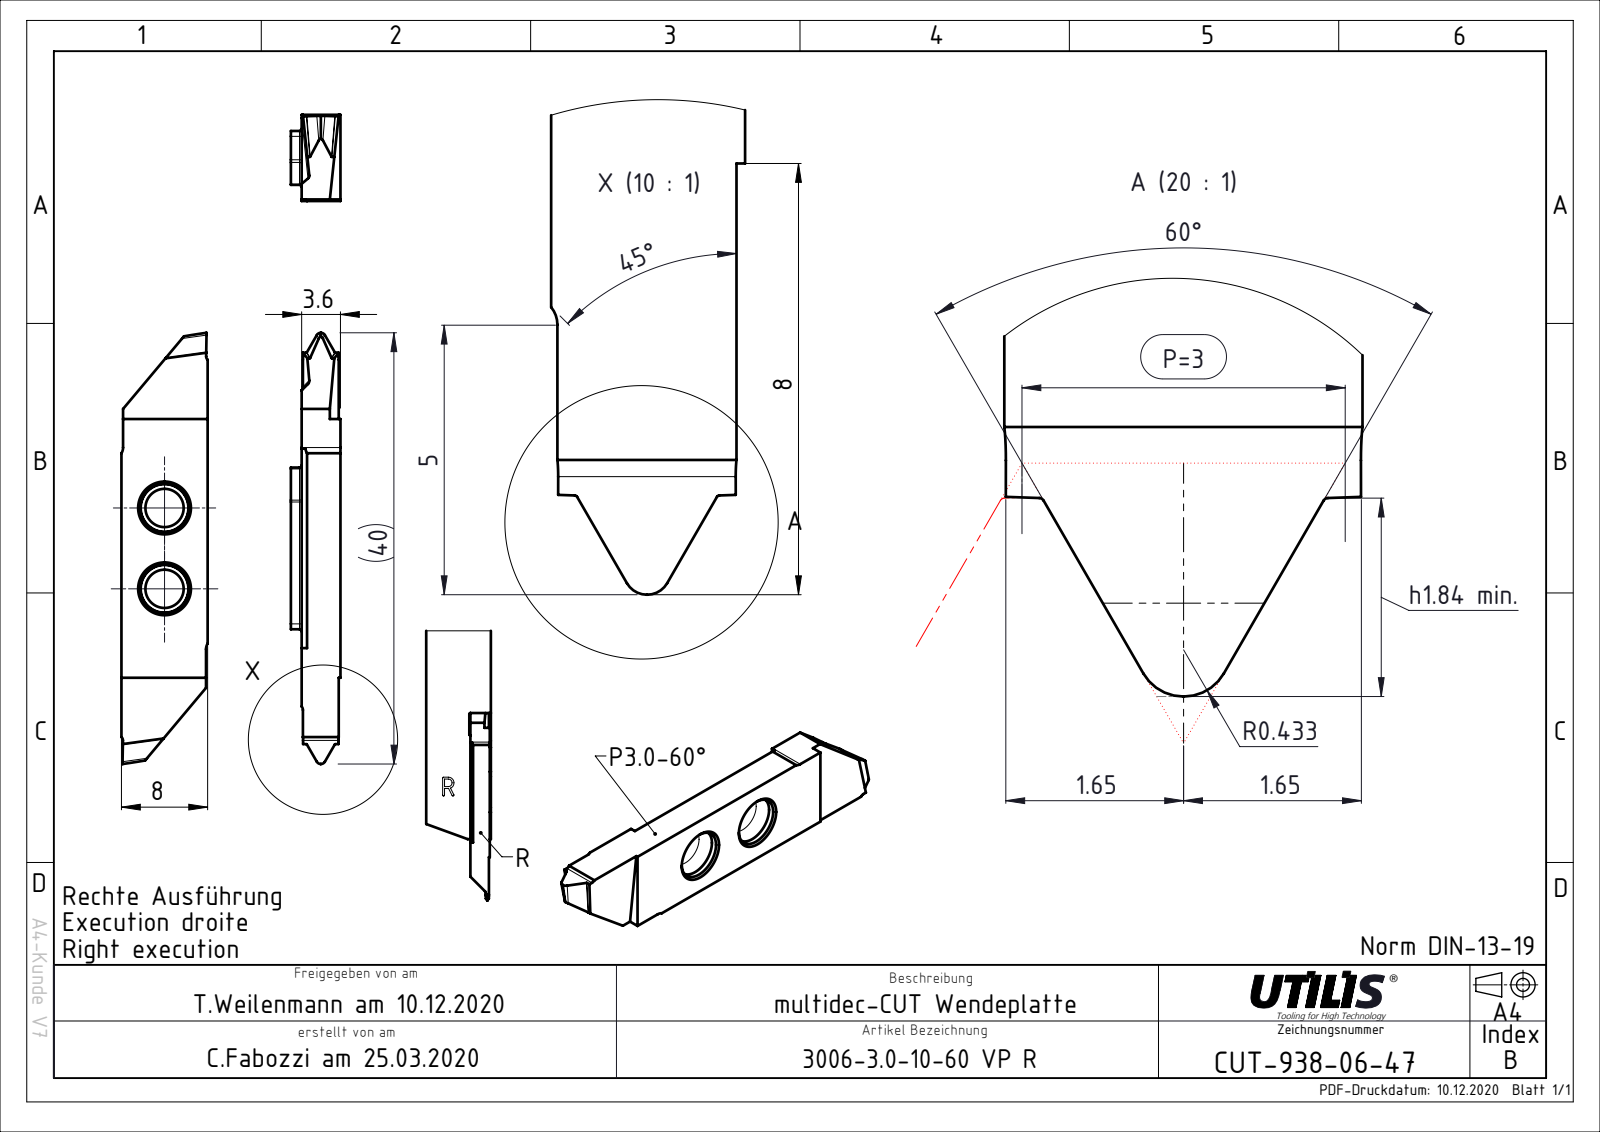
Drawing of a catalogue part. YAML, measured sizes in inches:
part_name: "CUT-938-06; ASME Y14.5"
step_written_by: "FormatWorks Professional (AP242_MANAGED_MODEL_BASED_3D_ENGINEERING_MIM_LF)"
units: inches
bodies: {solids: 1, faces: 50, planar: 32, cylindrical: 18, other: 0}
overall_size: [1.575, 0.315, 0.142]
volume: 0.053
surface_area: 1.35
round_holes:
  - {diameter: 0.14, count: 2}
partial_cylinders:
  - {radius: 0.017, count: 4}
  - {radius: 0.02, count: 2}
  - {radius: 0.039, count: 2}
face_to_face_distances: [0.142, 0.315, 0.124, 0.309, 0.887, 0.303, 0.994, 0.157, 0.163, 0.467]
hole_center_spacings: [0.295]
